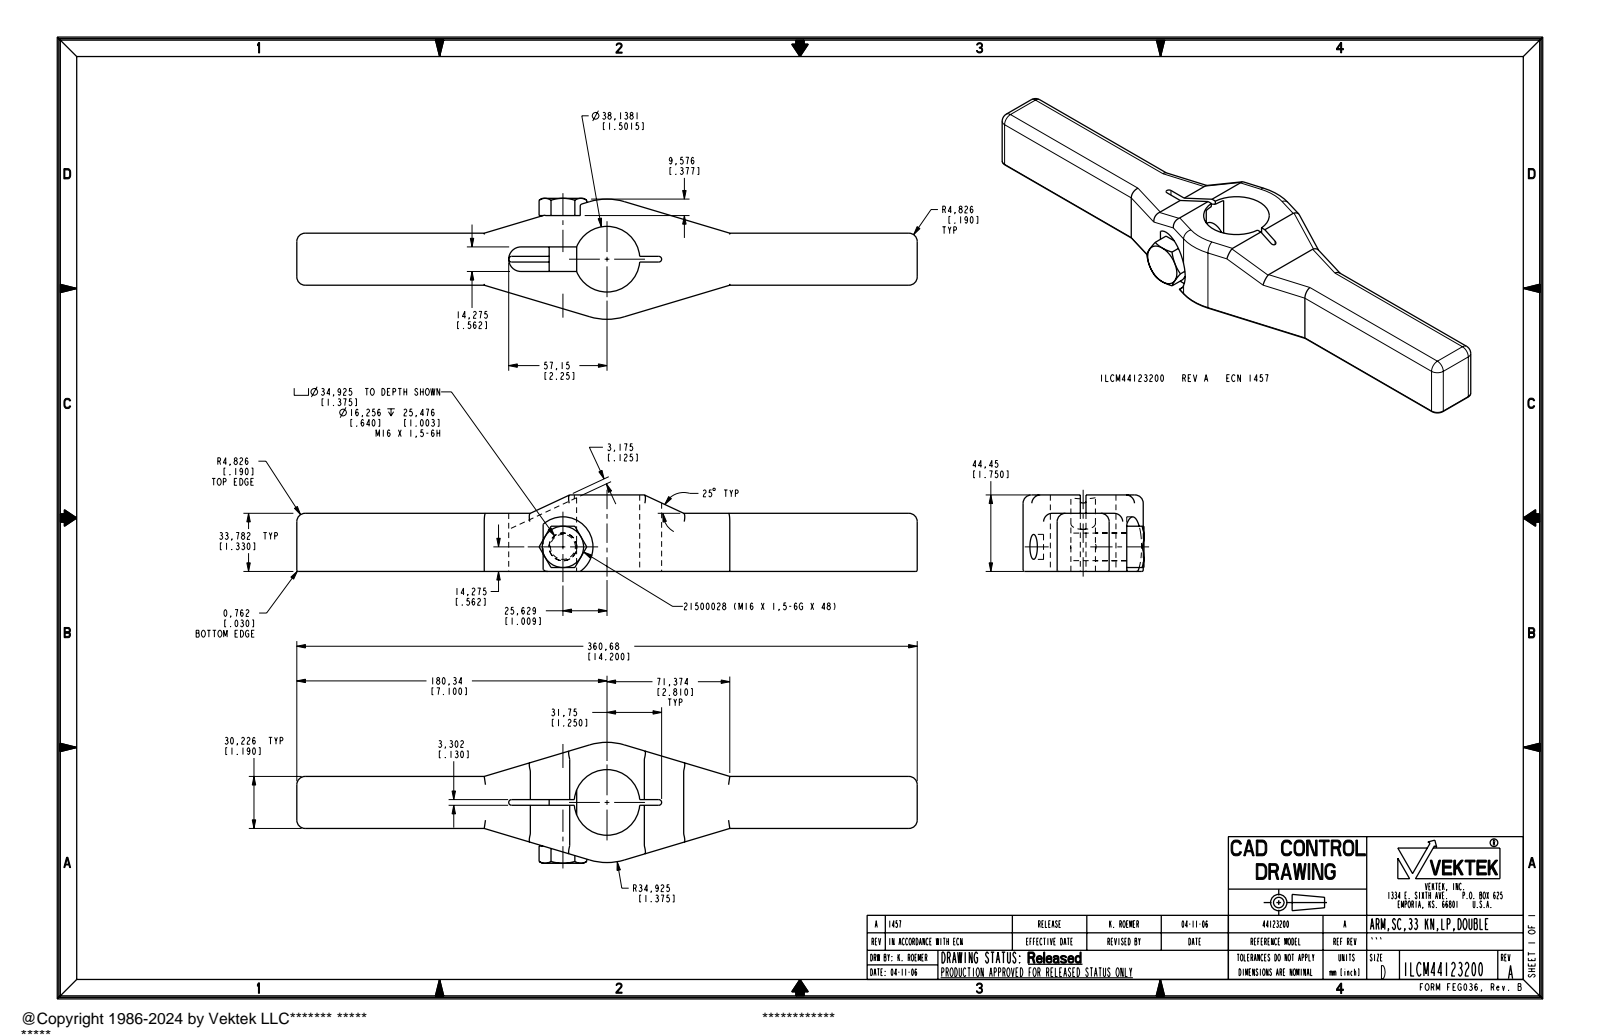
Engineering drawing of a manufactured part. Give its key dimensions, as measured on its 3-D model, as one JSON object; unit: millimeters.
{"part_name": "ILCM44123200", "step_written_by": "PRO/ENGINEER BY PARAMETRIC TECHNOLOGY CORPORATION, 2004290 (AUTOMOTIVE_DESIGN_CC2)", "units": "millimeters", "bodies": {"solids": 1, "faces": 104, "planar": 38, "cylindrical": 48, "other": 18}, "overall_size": [360.68, 70.28, 44.45], "volume_mm3": 442632, "surface_area_mm2": 64007, "round_holes": [[14.53, 1], [16.26, 1], [38.14, 1]], "round_bosses_or_shafts": [[16, 1]], "partial_cylinders_radius": [[4.83, 20], [0.76, 8], [1.65, 2], [7.14, 1], [17.46, 1], [34.92, 1]], "face_to_face_distances": [30.22, 33.78, 69.84, 7.97, 22.25, 44.45, 10.67, 69.78, 13.46, 16.76]}
